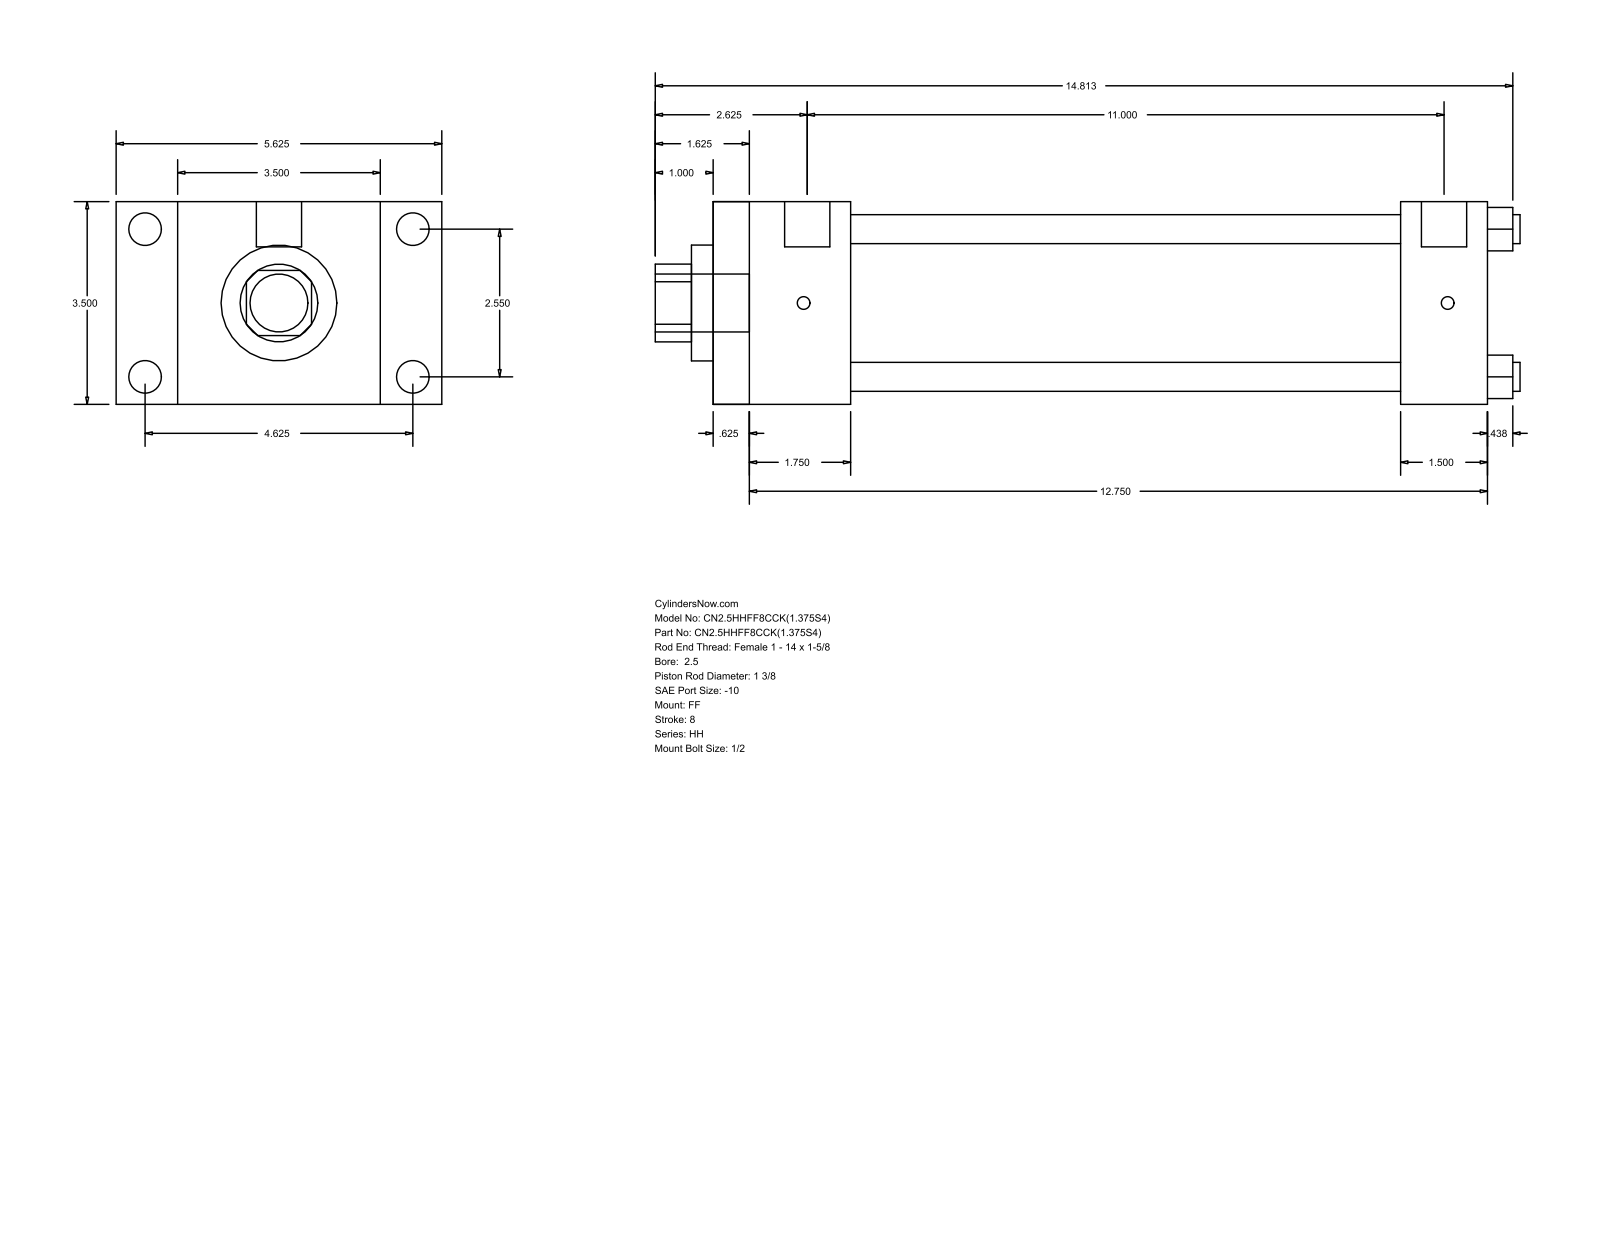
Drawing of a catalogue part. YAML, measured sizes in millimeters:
part_name: "HH_FF__0250_1.375"
step_written_by: "GSSL Pune (CONFIG_CONTROL_DESIGN)"
units: millimeters
bodies: {solids: 0, faces: 92, planar: 64, cylindrical: 28, other: 0}
overall_size: [379.41, 142.88, 88.9]
round_holes:
  - {diameter: 12.7, count: 4}
  - {diameter: 34.92, count: 1}
  - {diameter: 50.8, count: 1}
  - {diameter: 73.03, count: 1}
round_bosses_or_shafts:
  - {diameter: 14.3, count: 4}
  - {diameter: 5.56, count: 4}
  - {diameter: 19.84, count: 2}
  - {diameter: 25.4, count: 1}
partial_cylinders:
  - {radius: 17.06, count: 1}
face_to_face_distances: [88.9, 339.72, 15.87, 323.85, 60.32, 44.45, 279.4, 301.62, 285.75, 241.3]
hole_center_spacings: [45.79, 64.76, 91.58]
